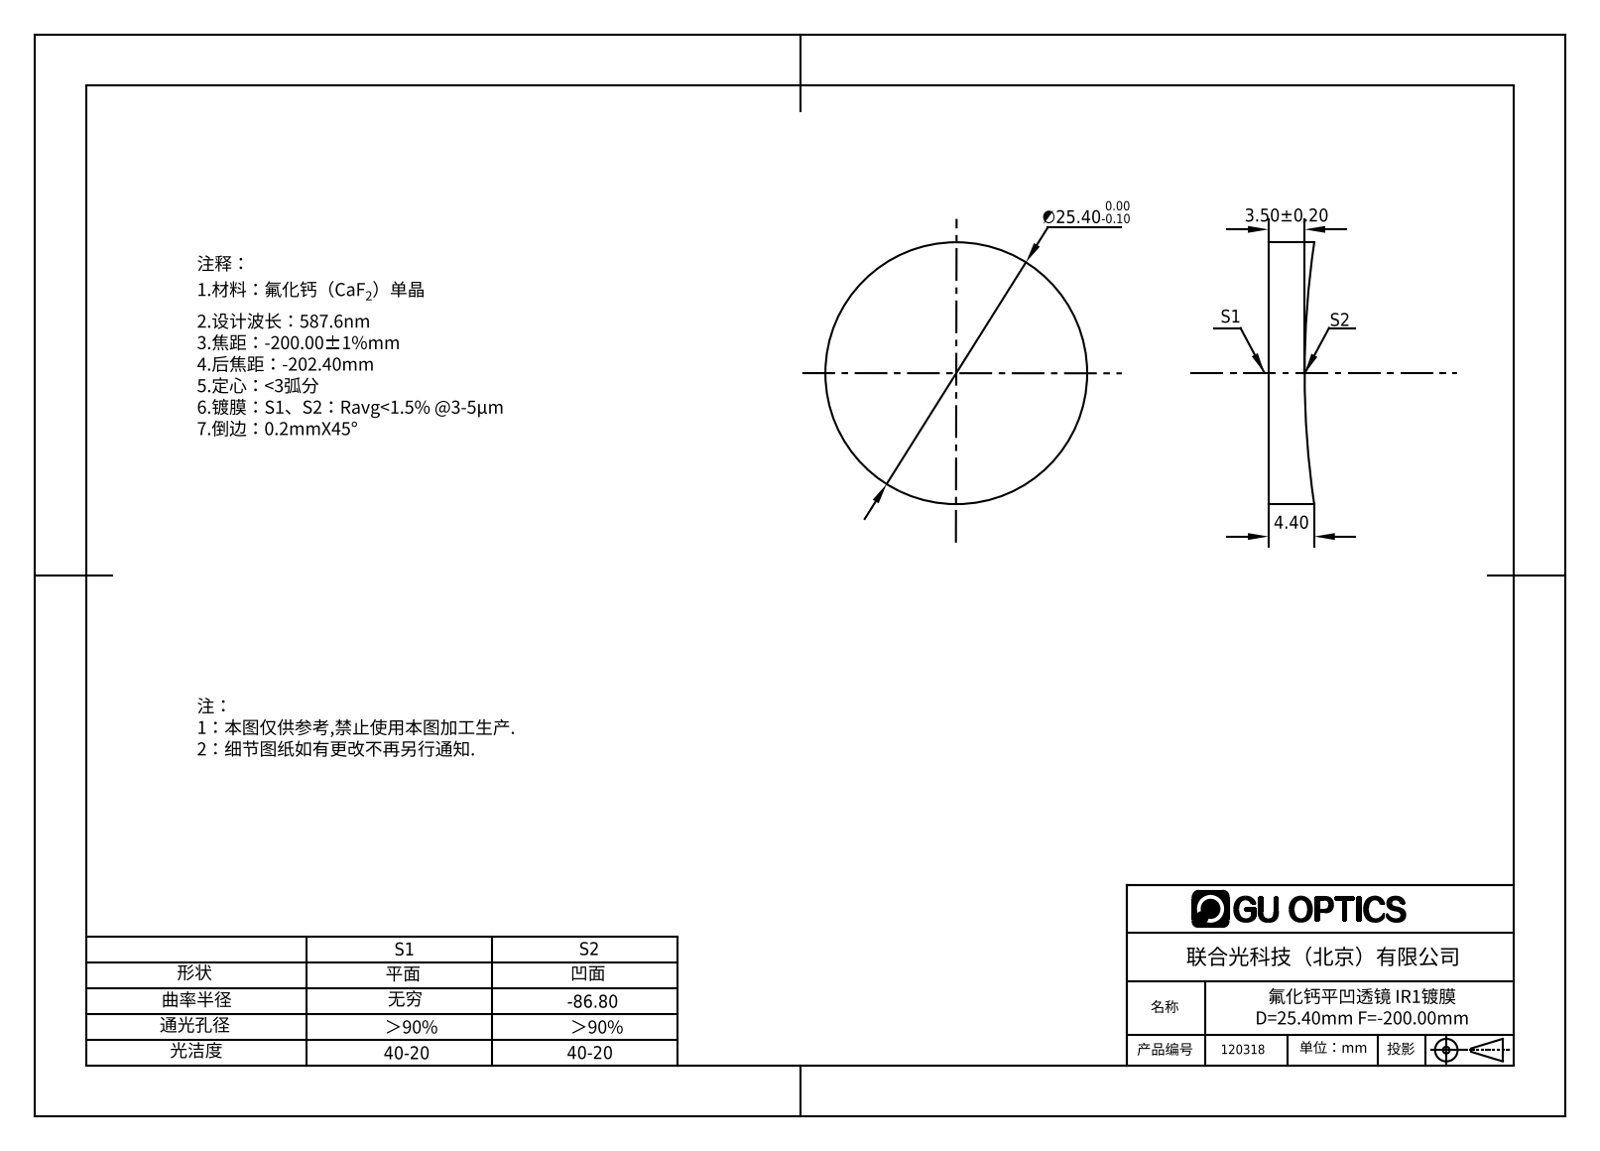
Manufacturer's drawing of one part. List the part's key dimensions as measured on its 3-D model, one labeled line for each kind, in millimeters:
Part name (STEP PRODUCT): 120311
STEP written by: SolidWorks 2016 (AUTOMOTIVE_DESIGN)
Units: millimetres
Bodies: 1 solid, 5 faces (1 planar, 2 cylindrical, 2 other)
Overall size (bounding box): 25.4 × 25.4 × 4.43
Volume: 2 010 mm³ · Surface area: 1 370 mm²
Round bosses / shafts (diameter × count): ⌀25.4 ×1
